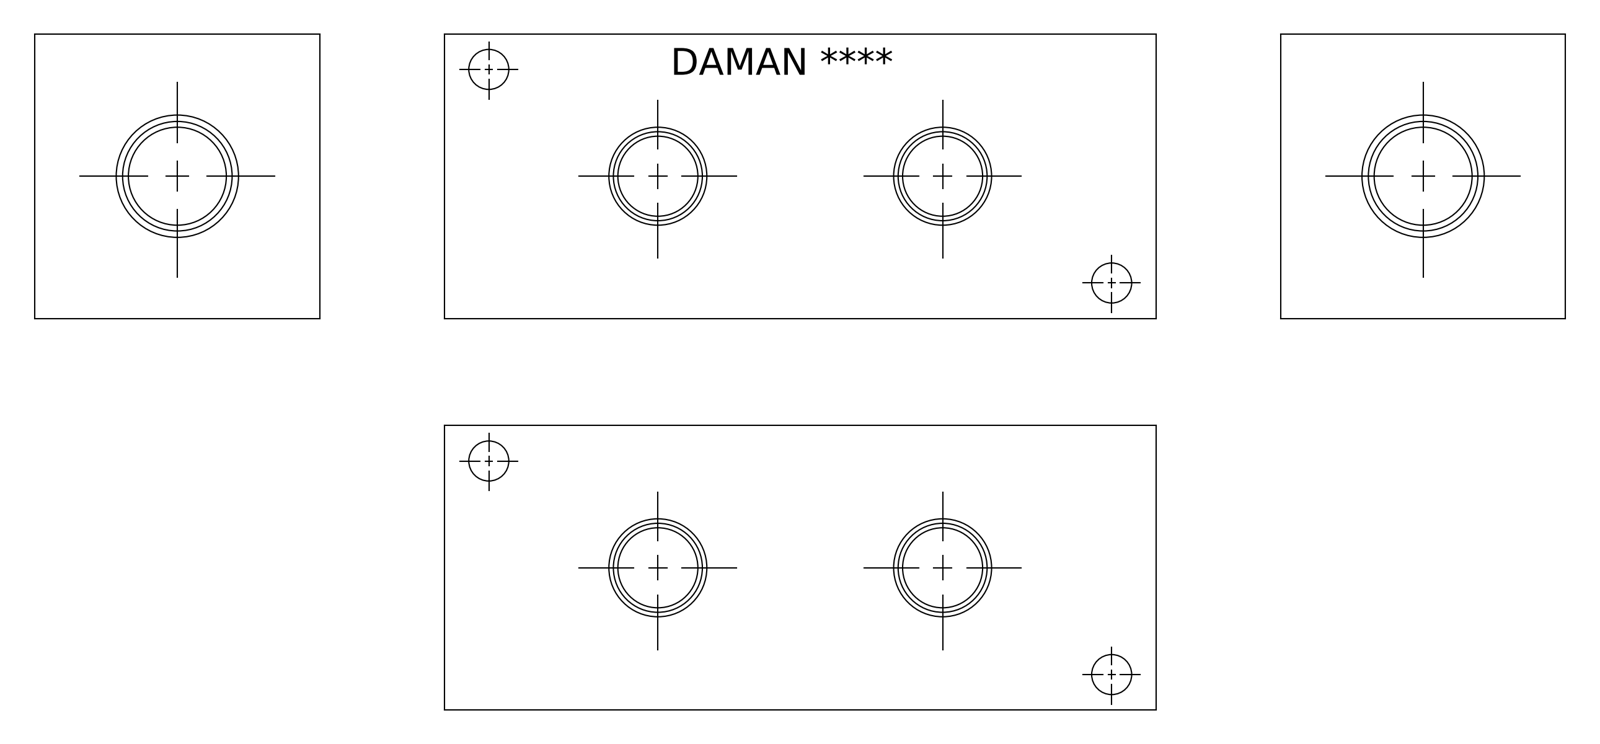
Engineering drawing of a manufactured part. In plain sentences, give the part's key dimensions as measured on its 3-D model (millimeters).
The part is named "Part_+H0900206P_3D". Its 3-D file was written by "Autodesk Inventor 2020 (AUTOMOTIVE_DESIGN)". It is 1 solid with 351 faces: 212 planar, 20 cylindrical and 119 other. Overall it measures 127 by 50.8 by 50.8 millimeters. Its volume is 295 612 cubic millimeters and its surface area 39 752 square millimeters. Round holes: 4 of diameter 7.14, 4 of diameter 14.3, 4 of diameter 17.3, 1 of diameter 17.48, 1 of diameter 21.59. The main face-to-face distances are 50.8, 127, 11.73, 39.07, 15.37, 111.63, 96.26, 50.76, 11.69, 0.64. The hole center spacings are 35.69, 83.19, 50.8, 117.51.
